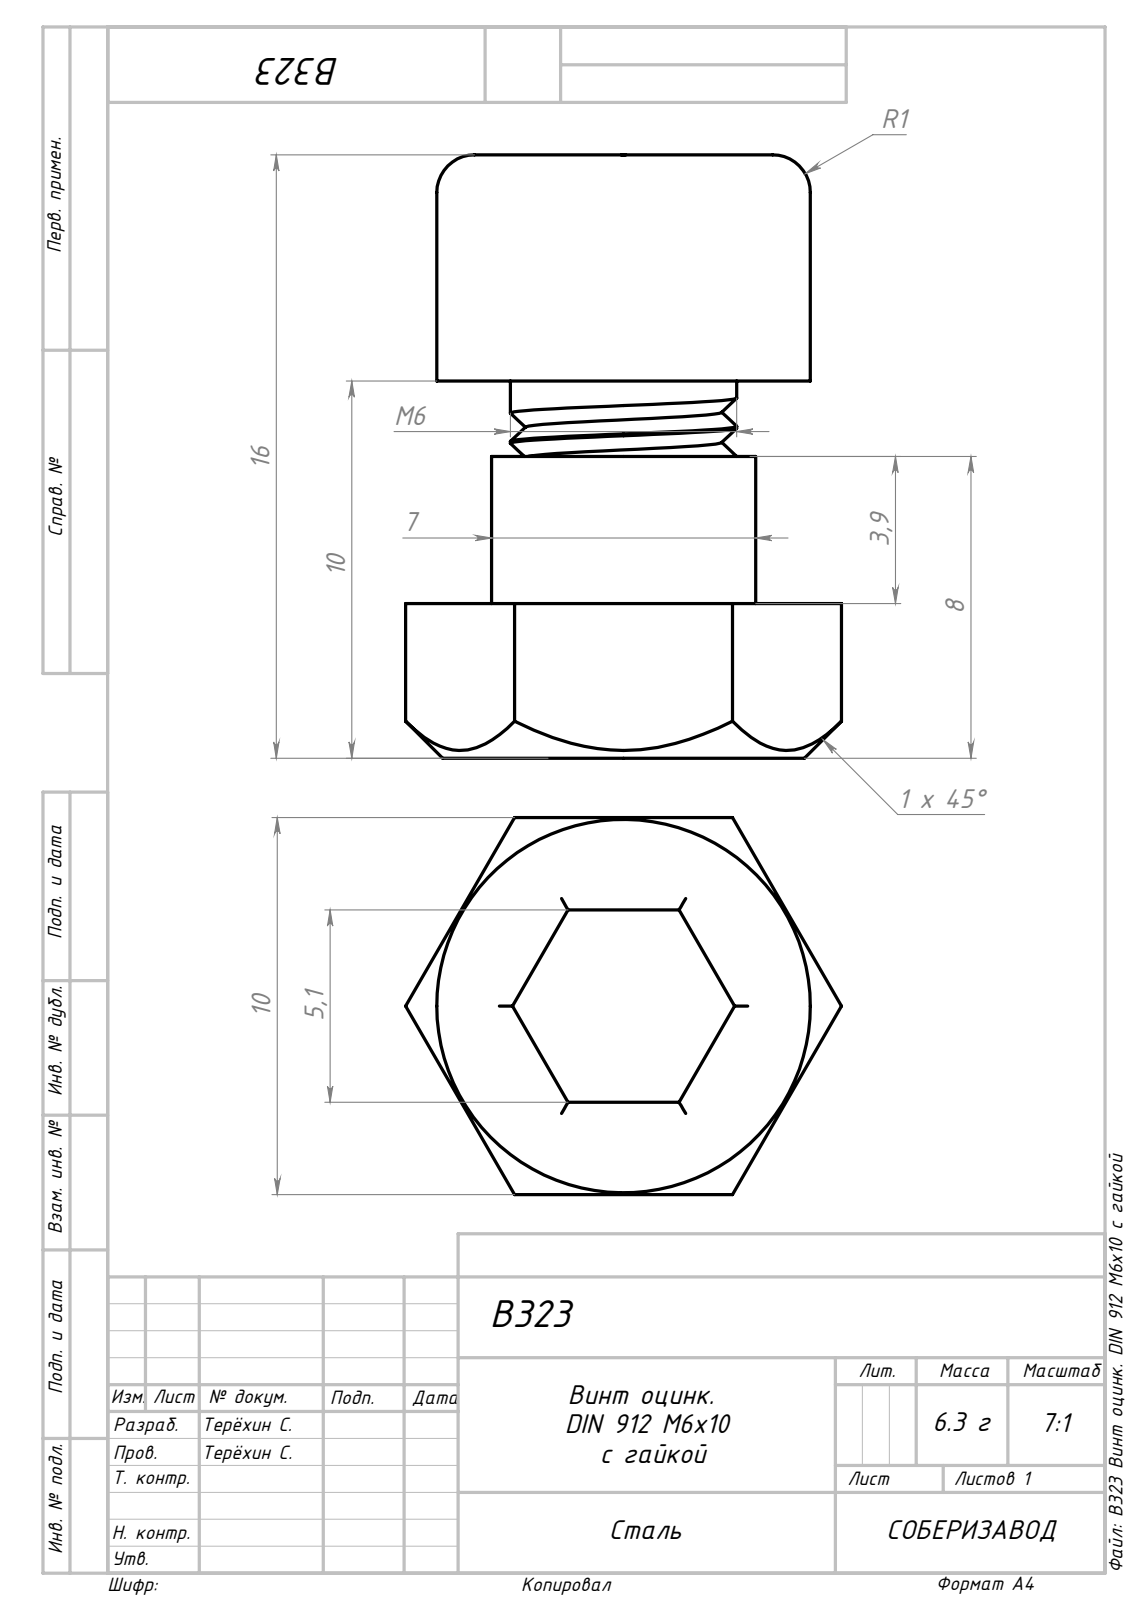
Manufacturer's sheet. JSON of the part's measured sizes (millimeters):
{"part_name": "B323 Винт оцинк. DIN 912 М6х10 с гайкой", "step_written_by": "SolidWorks 2022 (AUTOMOTIVE_DESIGN)", "units": "millimeters", "bodies": {"solids": 2, "faces": 95, "planar": 20, "cylindrical": 48, "other": 27}, "overall_size": [16, 11.55, 10], "volume_mm3": 909, "surface_area_mm2": 1144, "round_holes": [[5.3, 1]], "round_bosses_or_shafts": [[9.9, 1], [7, 1], [6, 1]], "partial_cylinders_radius": [[0.3, 6]], "face_to_face_distances": [10, 2.45, 7.55, 4.1, 5.9, 5.1, 2, 4, 12, 7.9]}
